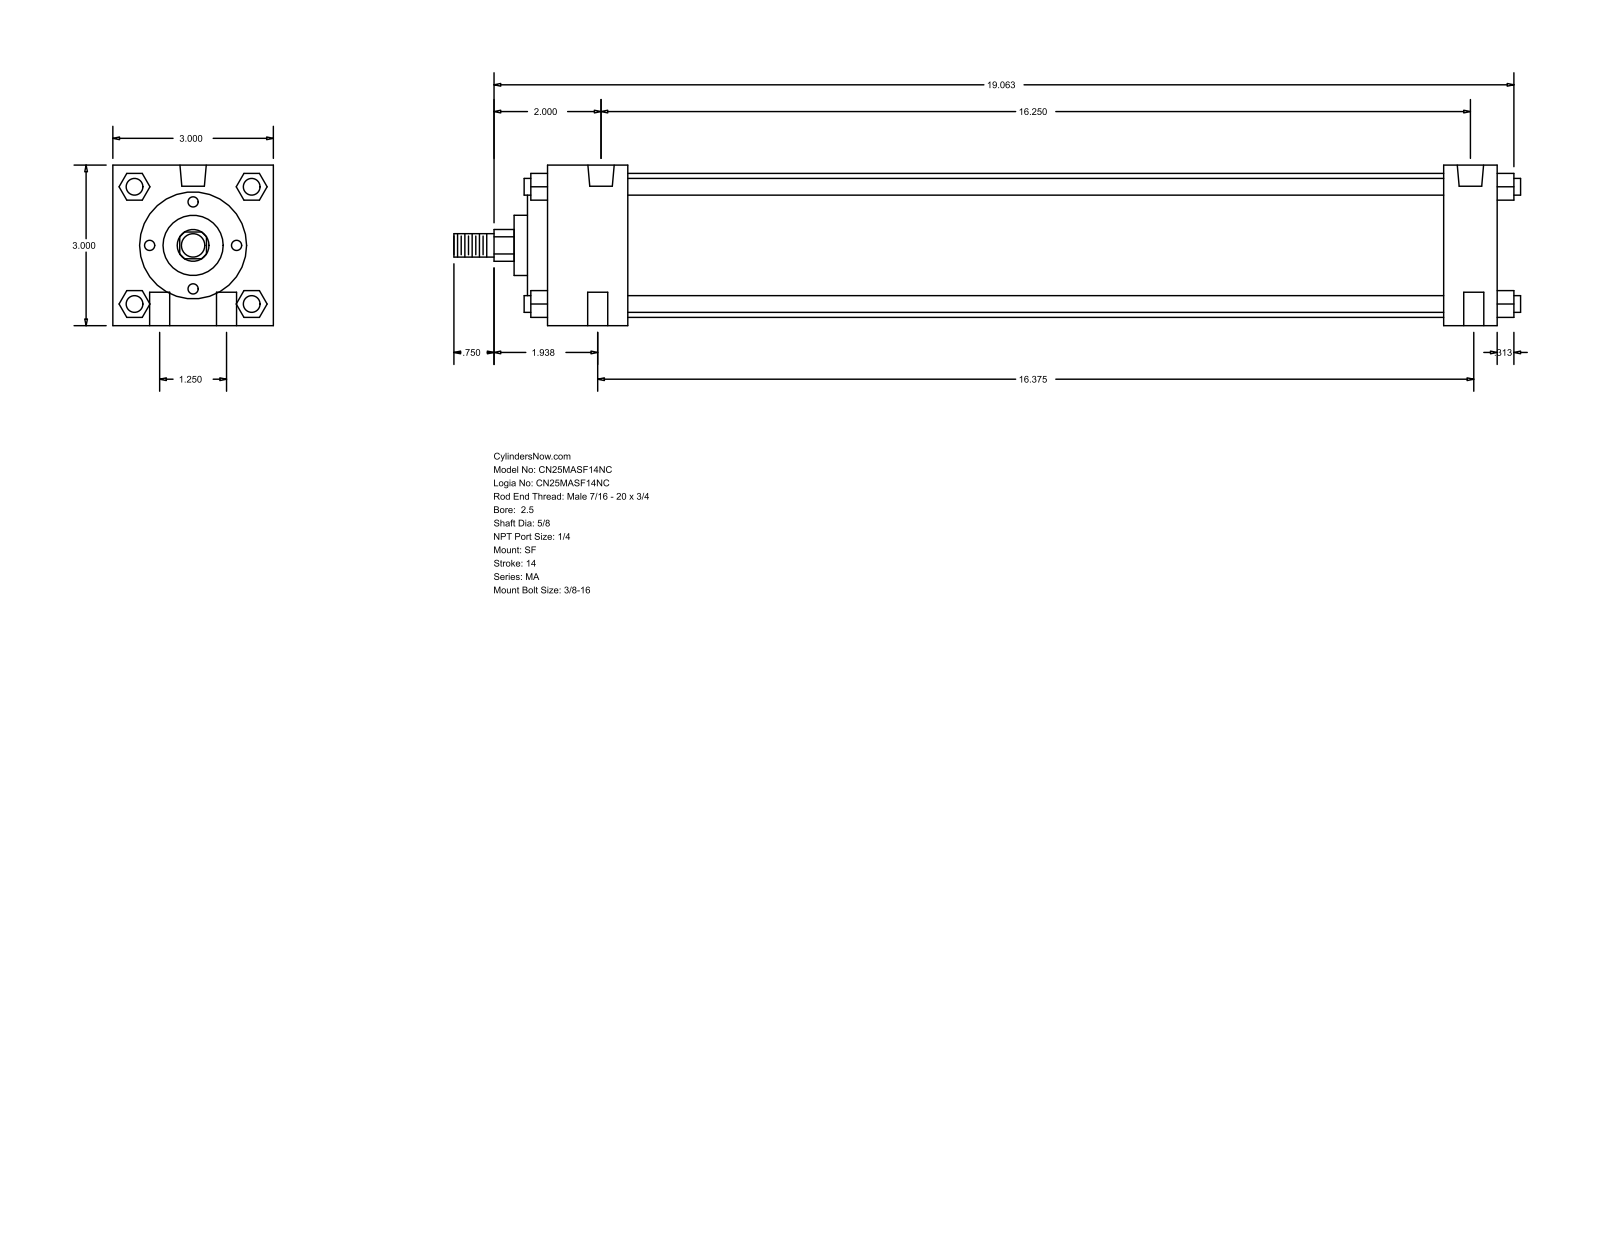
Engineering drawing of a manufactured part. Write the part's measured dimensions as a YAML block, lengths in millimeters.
part_name: "MA_SF__0250_0.625"
step_written_by: "GSSL Pune (CONFIG_CONTROL_DESIGN)"
units: millimeters
bodies: {solids: 0, faces: 126, planar: 95, cylindrical: 31, other: 0}
overall_size: [506.41, 76.2, 76.2]
round_holes:
  - {diameter: 9.53, count: 4}
  - {diameter: 7.94, count: 2}
  - {diameter: 12.49, count: 2}
round_bosses_or_shafts:
  - {diameter: 7.94, count: 4}
  - {diameter: 68.33, count: 1}
  - {diameter: 50.8, count: 1}
  - {diameter: 28.57, count: 1}
  - {diameter: 15.88, count: 1}
  - {diameter: 11.11, count: 1}
partial_cylinders:
  - {radius: 7.54, count: 1}
face_to_face_distances: [76.2, 450.85, 25.4, 425.45, 38.1, 387.35, 412.75, 12.7, 9.52, 47.62]
hole_center_spacings: [15.96, 414.64, 31.76, 412.75, 415.93, 417.14]
